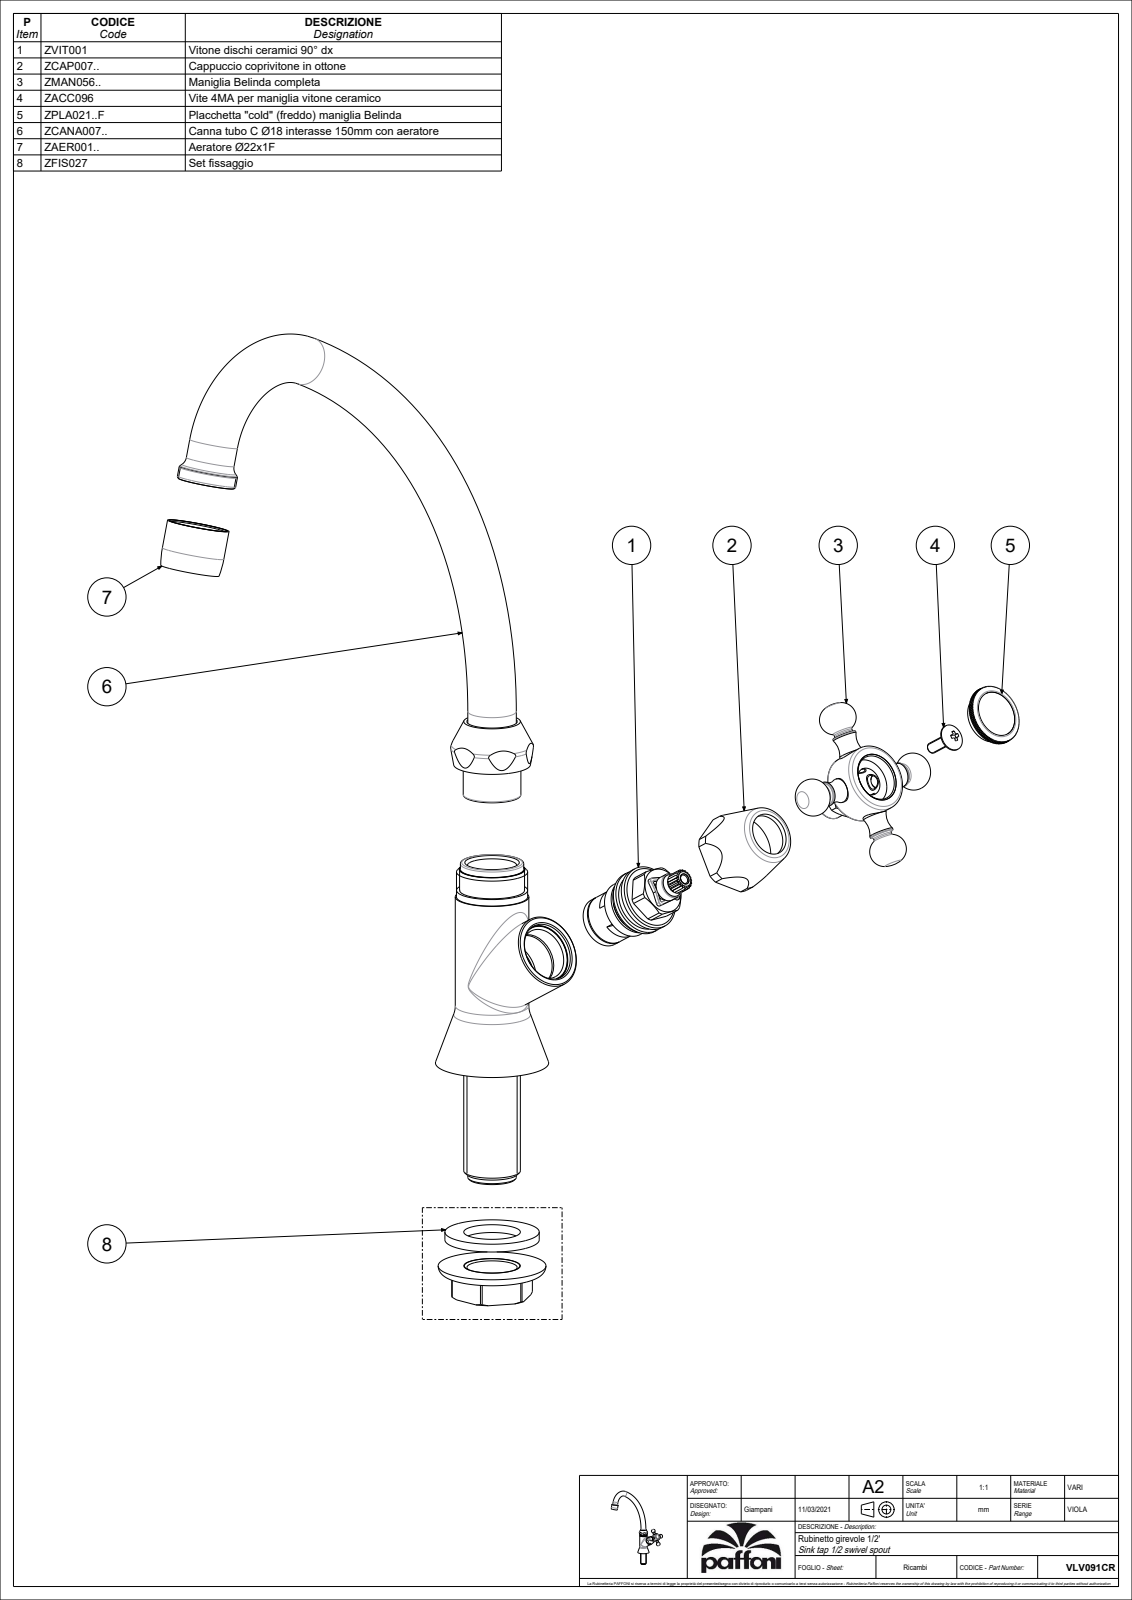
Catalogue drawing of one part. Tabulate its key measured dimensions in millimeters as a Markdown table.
| quantity | value |
| --- | --- |
| part name | VLV091CR |
| STEP written by | CREO PARAMETRIC BY PTC INC, 2020044 (CONFIG_CONTROL_DESIGN) |
| units | millimeters |
| bodies | 1 solid, 491 faces (235 planar, 152 cylindrical, 104 other) |
| overall size | 255.5 × 196.03 × 105.57 |
| volume | 173 597 mm³ |
| surface area | 35 306 mm² |
| round bosses / shafts (diameter × count) | 18 × 2, 9 × 2, 7 × 2, 27.3 × 1, 27.2 × 1, 26.4 × 1, 25 × 1, 23.2 × 1 |
| partial cylindrical surfaces (radius × count) | 11 × 1, 14.5 × 1 |
| main face-to-face distances | 26.5, 5.75, 20.75, 29, 11.2, 16.5, 1.25, 27.75, 22, 15 |
